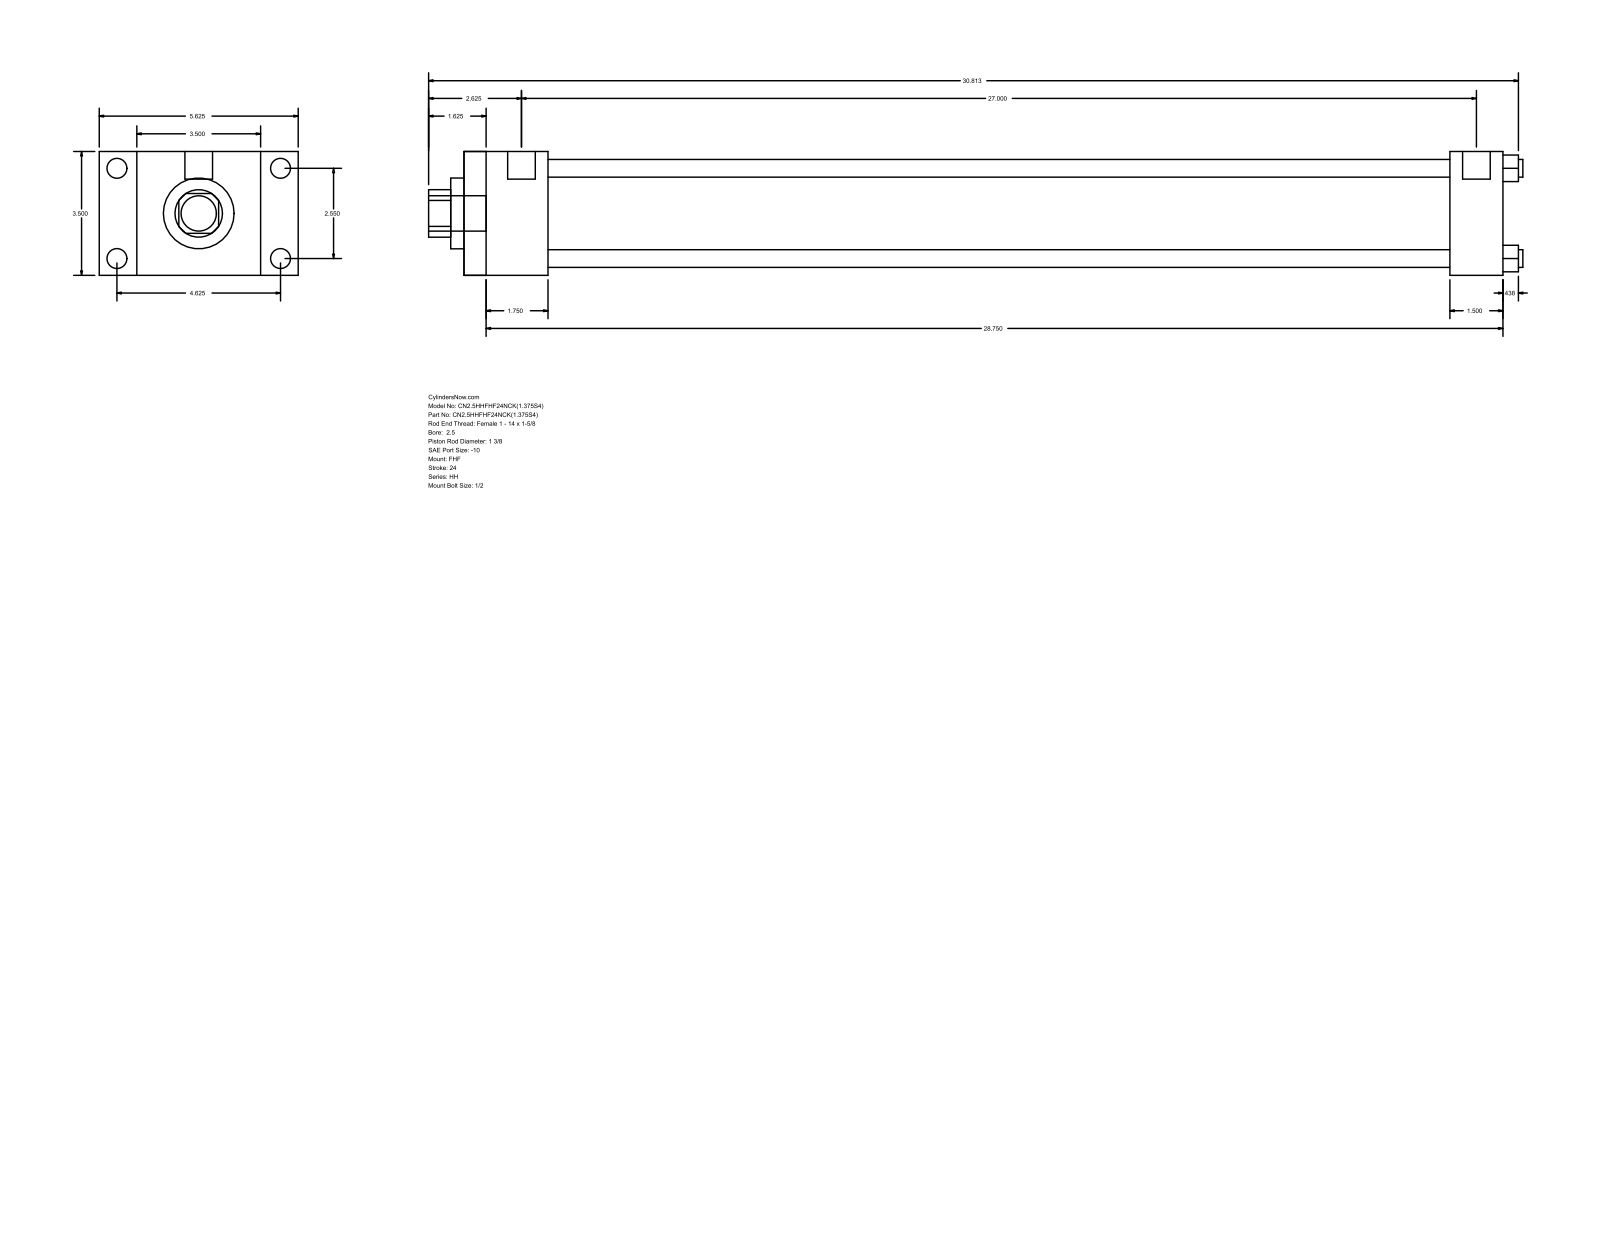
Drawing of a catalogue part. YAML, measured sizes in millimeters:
part_name: "HH_FHF__0250_1.375"
step_written_by: "GSSL Pune (CONFIG_CONTROL_DESIGN)"
units: millimeters
bodies: {solids: 0, faces: 88, planar: 60, cylindrical: 28, other: 0}
overall_size: [785.81, 142.88, 88.9]
round_holes:
  - {diameter: 12.7, count: 4}
  - {diameter: 34.92, count: 1}
  - {diameter: 50.8, count: 1}
  - {diameter: 73.03, count: 1}
round_bosses_or_shafts:
  - {diameter: 14.3, count: 4}
  - {diameter: 5.56, count: 4}
  - {diameter: 19.84, count: 2}
  - {diameter: 25.4, count: 1}
partial_cylinders:
  - {radius: 17.06, count: 1}
face_to_face_distances: [88.9, 60.32, 26.99, 115.89, 746.12, 685.8, 142.88, 708.02, 647.7, 38.1]
hole_center_spacings: [45.79, 64.76, 91.58]
